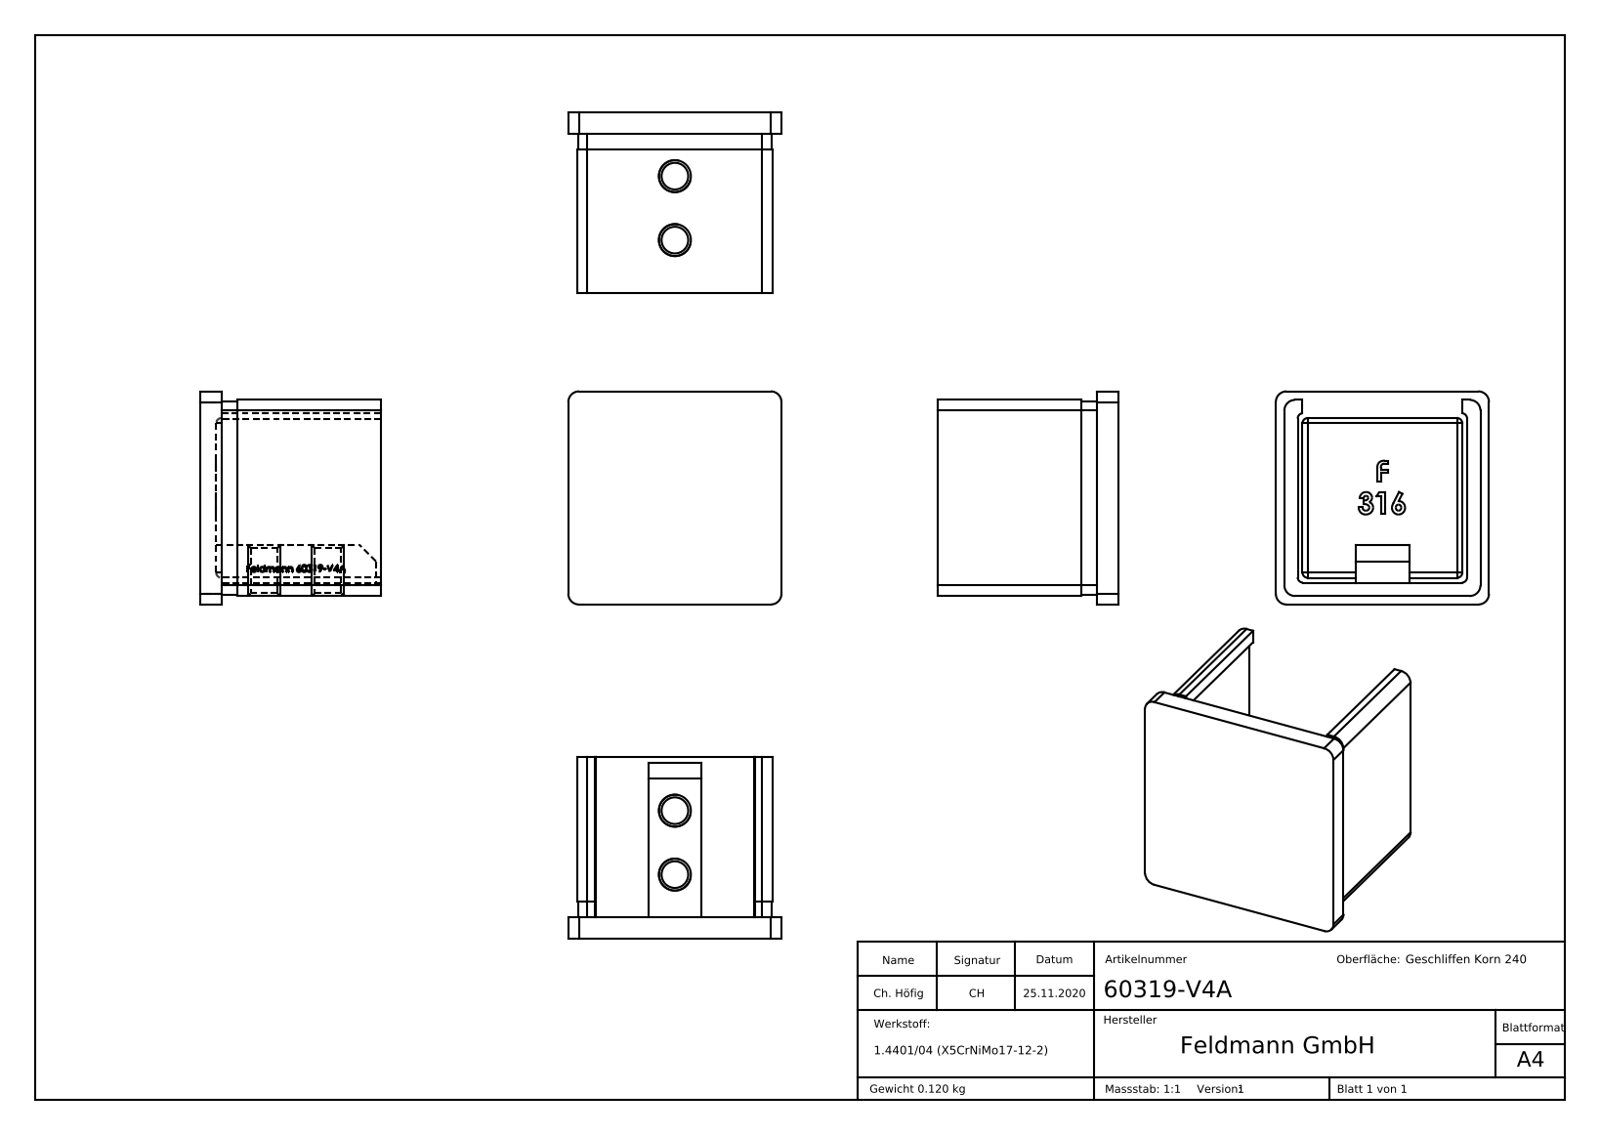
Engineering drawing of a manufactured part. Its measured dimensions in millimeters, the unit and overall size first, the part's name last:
Units: millimetres
Overall size (bounding box): 40 × 40 × 34
Round holes (diameter × count): ⌀5 ×2
Partial cylindrical surfaces — rounded edges, fillets, slot ends (radius × count): R1 ×8, R2 ×8, R1.75 ×4
Main face-to-face distances: 2.5, 34.3, 36.8, 31.8, 3, 1.6, 38.4, 1, 4, 4.1
Hole centre spacings: 12
Volume: 15 050 mm³ · Surface area: 10 978 mm²
Bodies: 1 solid, 342 faces (193 planar, 25 cylindrical, 124 other)
Part name (STEP PRODUCT): 60319-V4A
STEP written by: SolidWorks 2018 (CONFIG_CONTROL_DESIGN)
